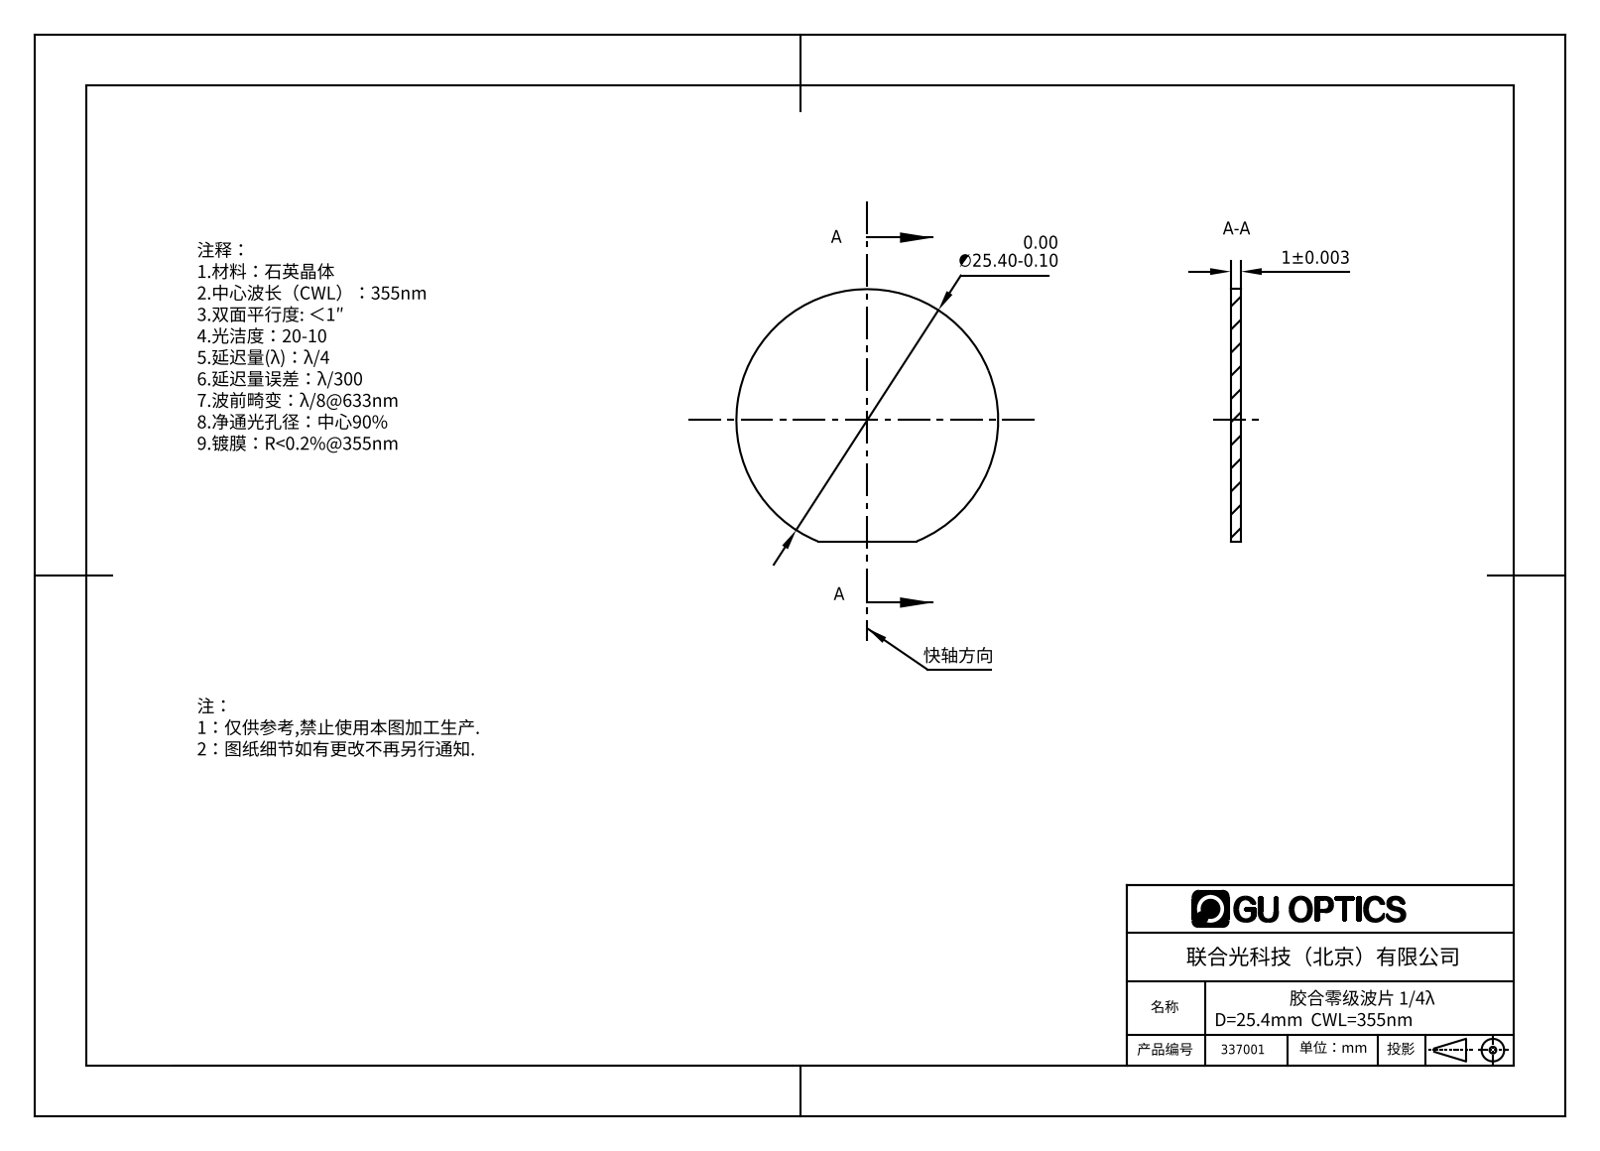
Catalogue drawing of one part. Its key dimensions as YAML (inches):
part_name: "336001"
step_written_by: "SolidWorks 2019 (AUTOMOTIVE_DESIGN)"
units: inches
bodies: {solids: 1, faces: 6, planar: 3, cylindrical: 3, other: 0}
overall_size: [1, 0.963, 0.039]
volume: 0.031
surface_area: 1.676
round_bosses_or_shafts:
  - {diameter: 1, count: 1}
face_to_face_distances: [0.039]
